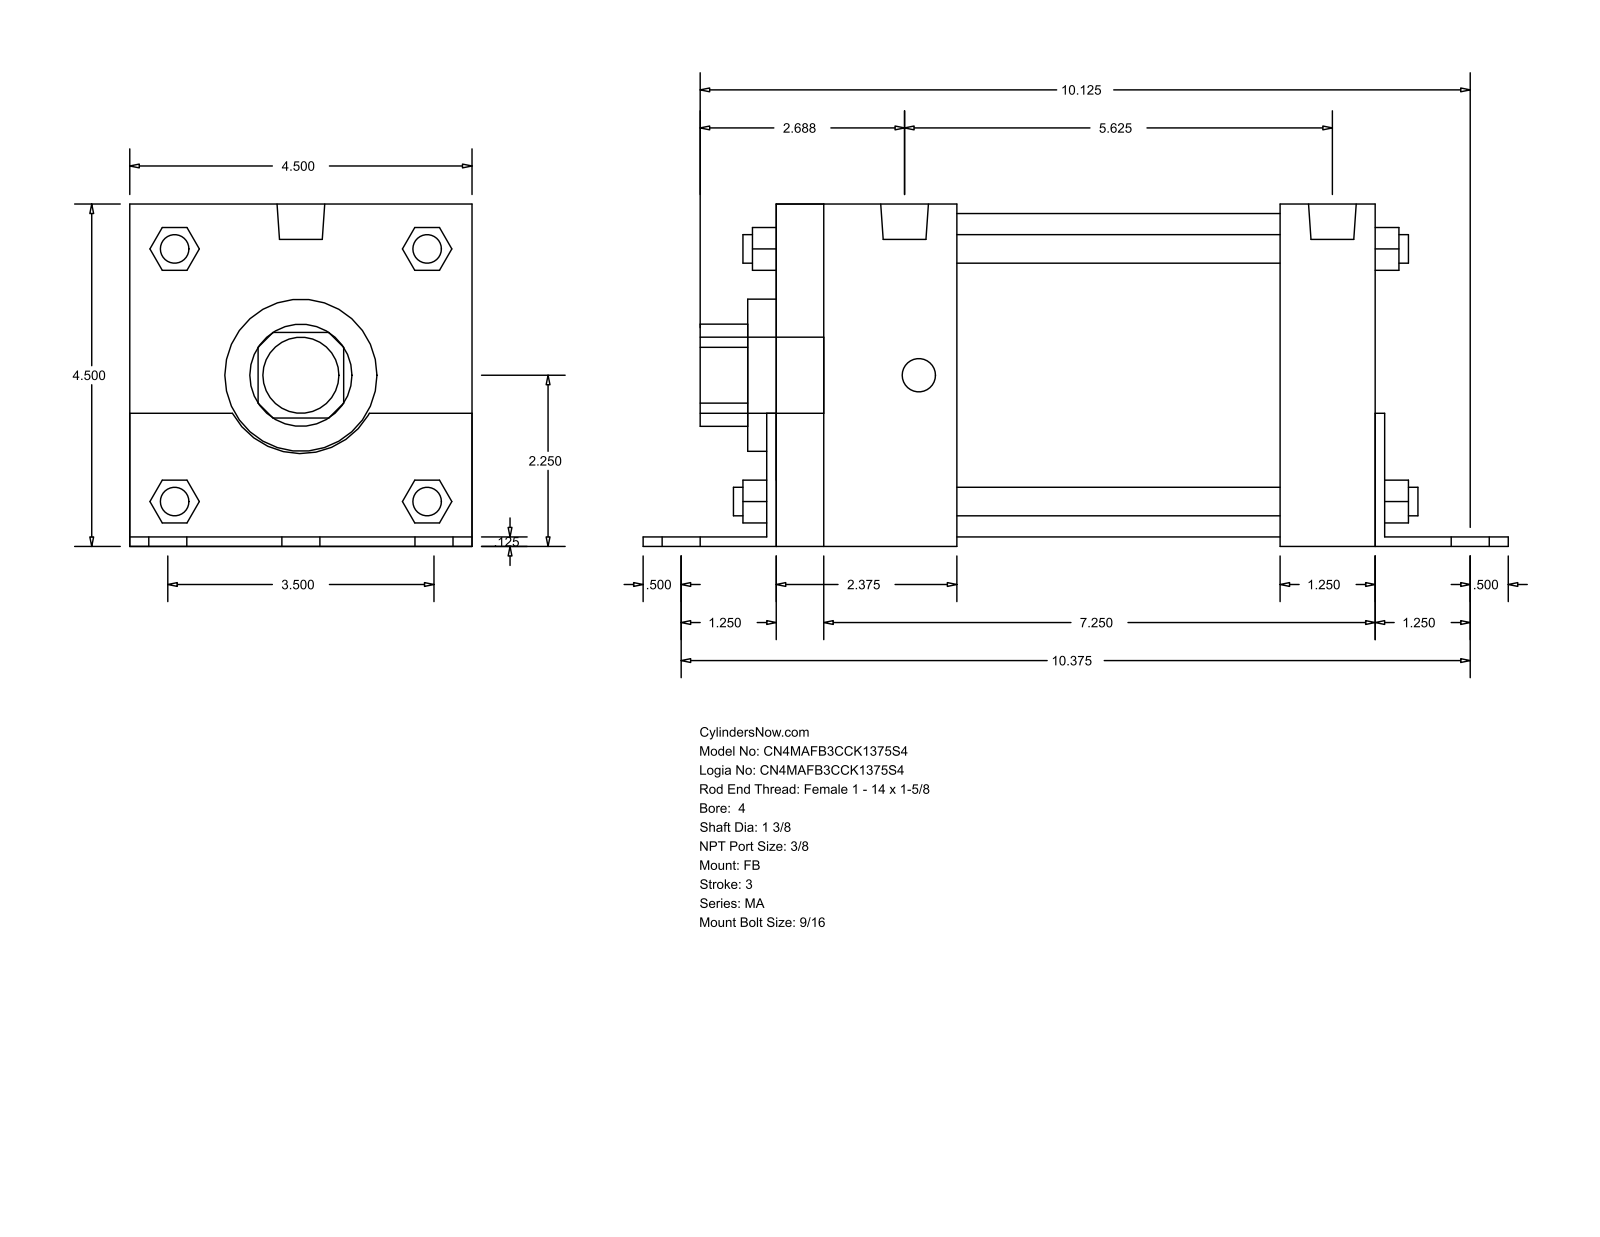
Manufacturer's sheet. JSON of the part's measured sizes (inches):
{"part_name": "MA_FB__0400_1.375", "step_written_by": "GSSL Pune (CONFIG_CONTROL_DESIGN)", "units": "inches", "bodies": {"solids": 0, "faces": 140, "planar": 105, "cylindrical": 35, "other": 0}, "overall_size": [11.375, 4.502, 4.5], "round_holes": [[1.375, 1], [2, 1], [4.25, 1]], "round_bosses_or_shafts": [[0.563, 6], [0.437, 4], [0.375, 4], [0.627, 2], [1, 1]], "partial_cylinders_radius": [[0.672, 1], [1.03, 1]], "face_to_face_distances": [4.5, 0.125, 4.502, 0.123, 4.377, 8, 7.875, 2.375, 8.125, 1.25]}
